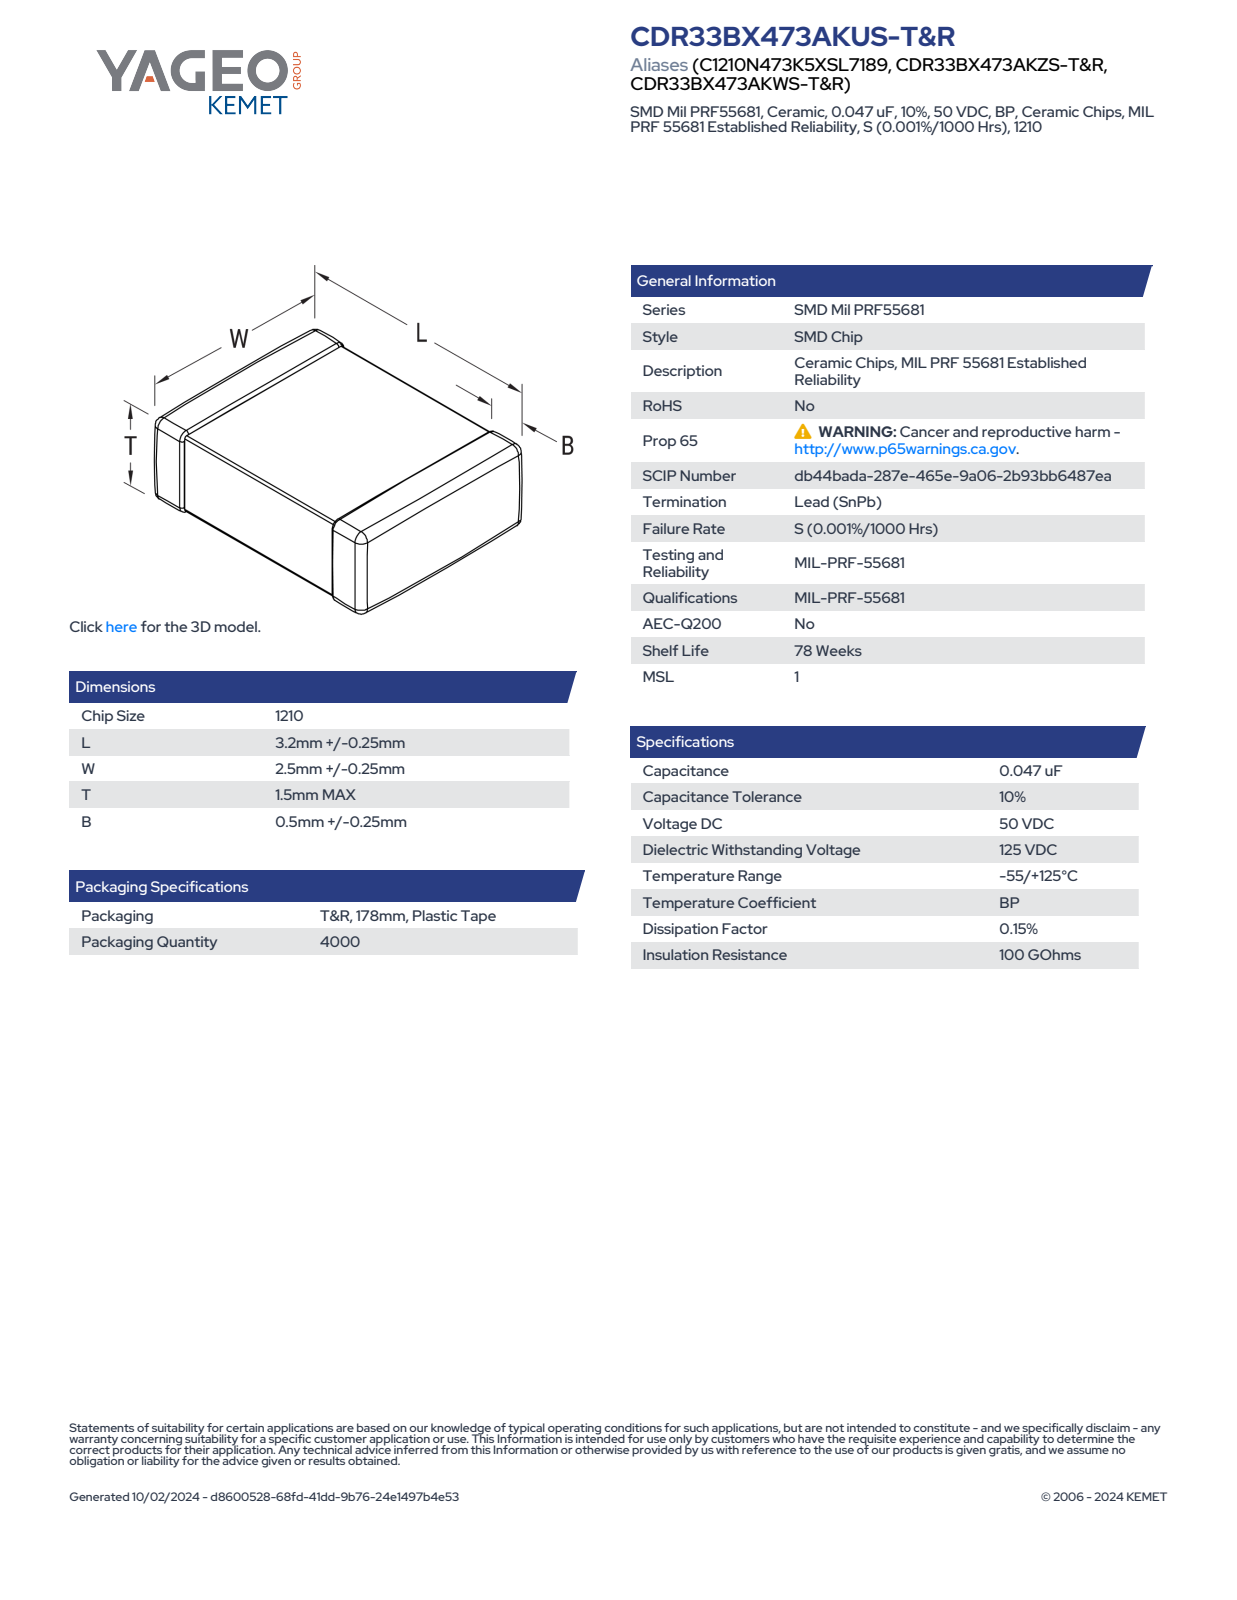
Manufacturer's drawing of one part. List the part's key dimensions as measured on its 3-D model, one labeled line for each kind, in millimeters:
Part name (STEP PRODUCT): CCS_STDNOS_1210_L3.45W2.75T1.5B0.75
STEP written by: SolidWorks 2021 (AUTOMOTIVE_DESIGN)
Units: millimetres
Bodies: 4 solids, 125 faces (71 planar, 38 cylindrical, 16 other)
Overall size (bounding box): 3.45 × 2.75 × 1.5
Volume: 13 mm³ · Surface area: 37 mm²
Main face-to-face distances: 1.44, 1.38, 3.45, 2.69, 1.5, 2.63, 2.75, 1.45, 1.39, 1.33
